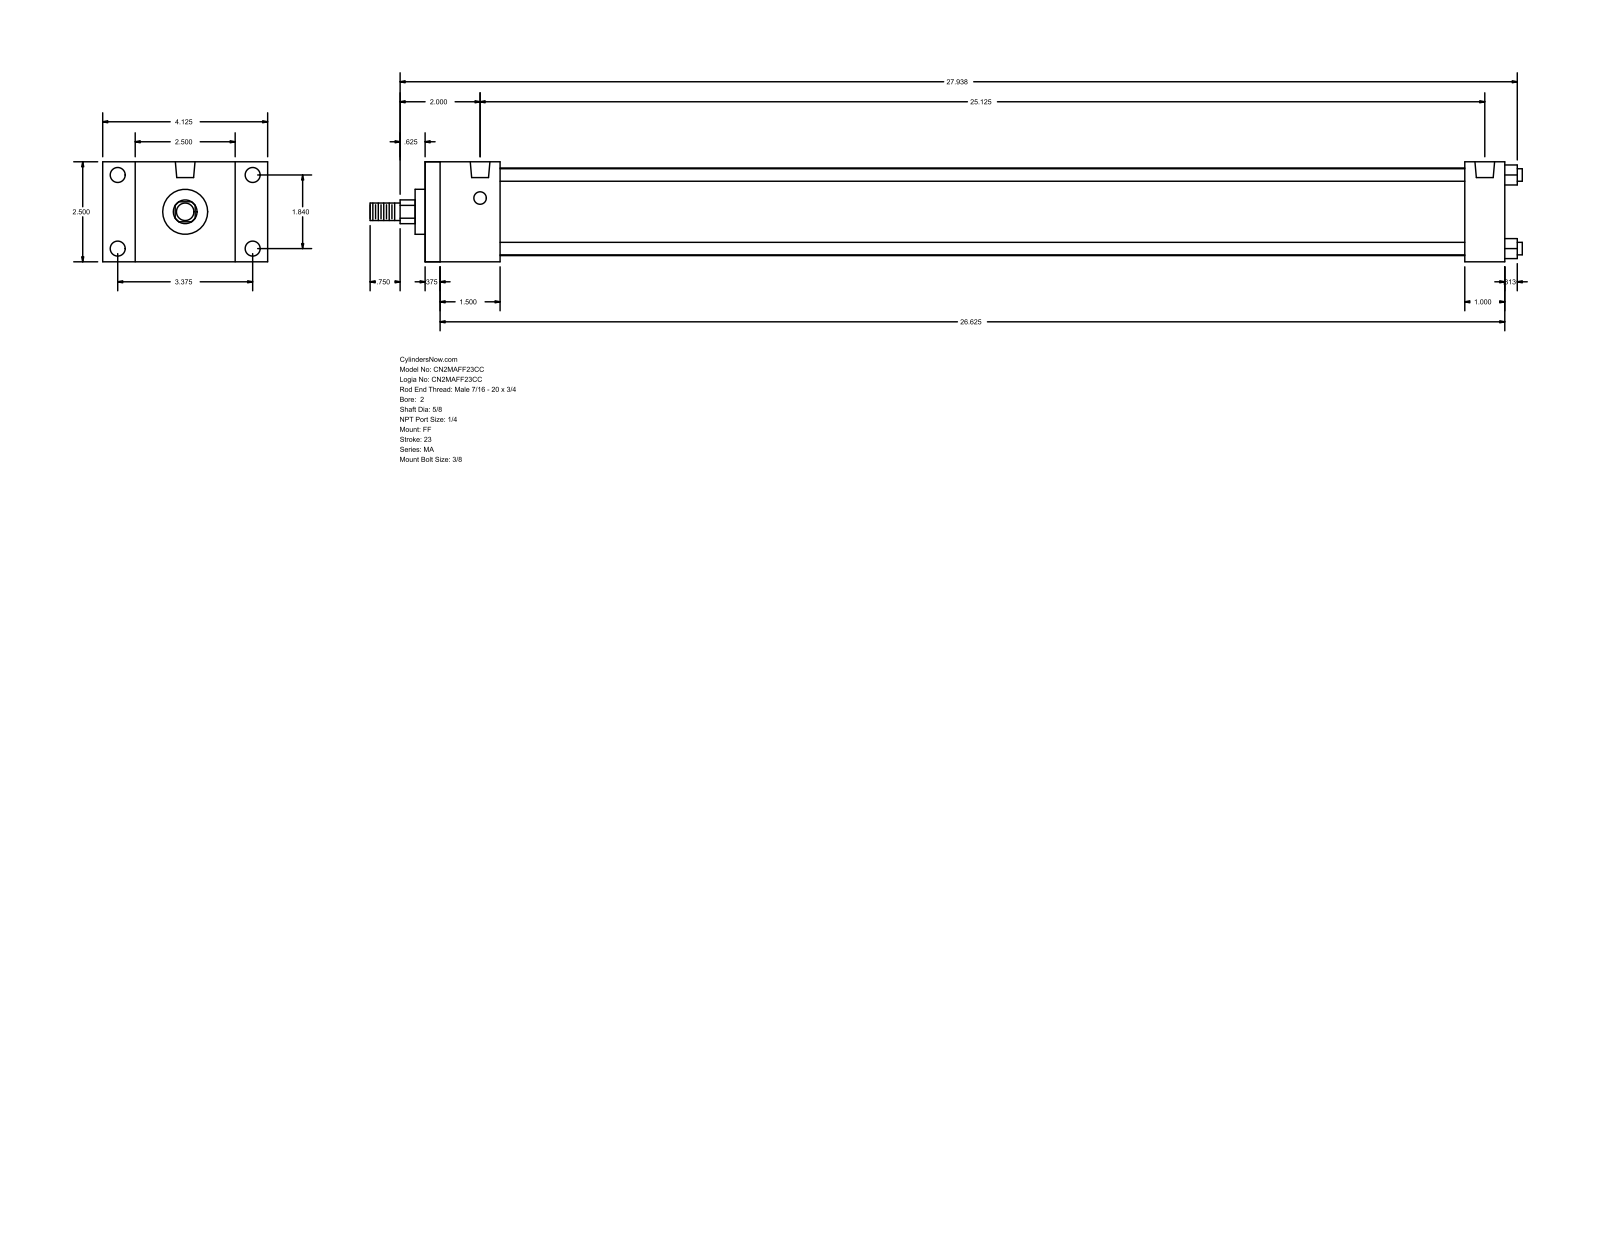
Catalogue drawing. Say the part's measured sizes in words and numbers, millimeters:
The part is named "MA_FF__0200_0.625". Its 3-D file was written by "GSSL Pune (CONFIG_CONTROL_DESIGN)". It is 0 solids with 92 faces: 64 planar, 28 cylindrical and 0 other. Overall it measures 731.84 by 104.78 by 63.5 millimeters. Round holes: 4 of diameter 7.94, 4 of diameter 9.53, 2 of diameter 12.49. Round bosses or shafts: 4 of diameter 7.94, 1 of diameter 55.63, 1 of diameter 28.57, 1 of diameter 15.88, 1 of diameter 11.11. Partial cylindrical surfaces (rounded edges, fillets, slot ends): 1 of radius 7.54. The main face-to-face distances are 63.5, 685.79, 676.27, 9.52, 25.4, 38.1, 47.62, 660.39, 650.87, 612.77. The hole center spacings are 46.74, 85.72, 97.63, 638.18.
